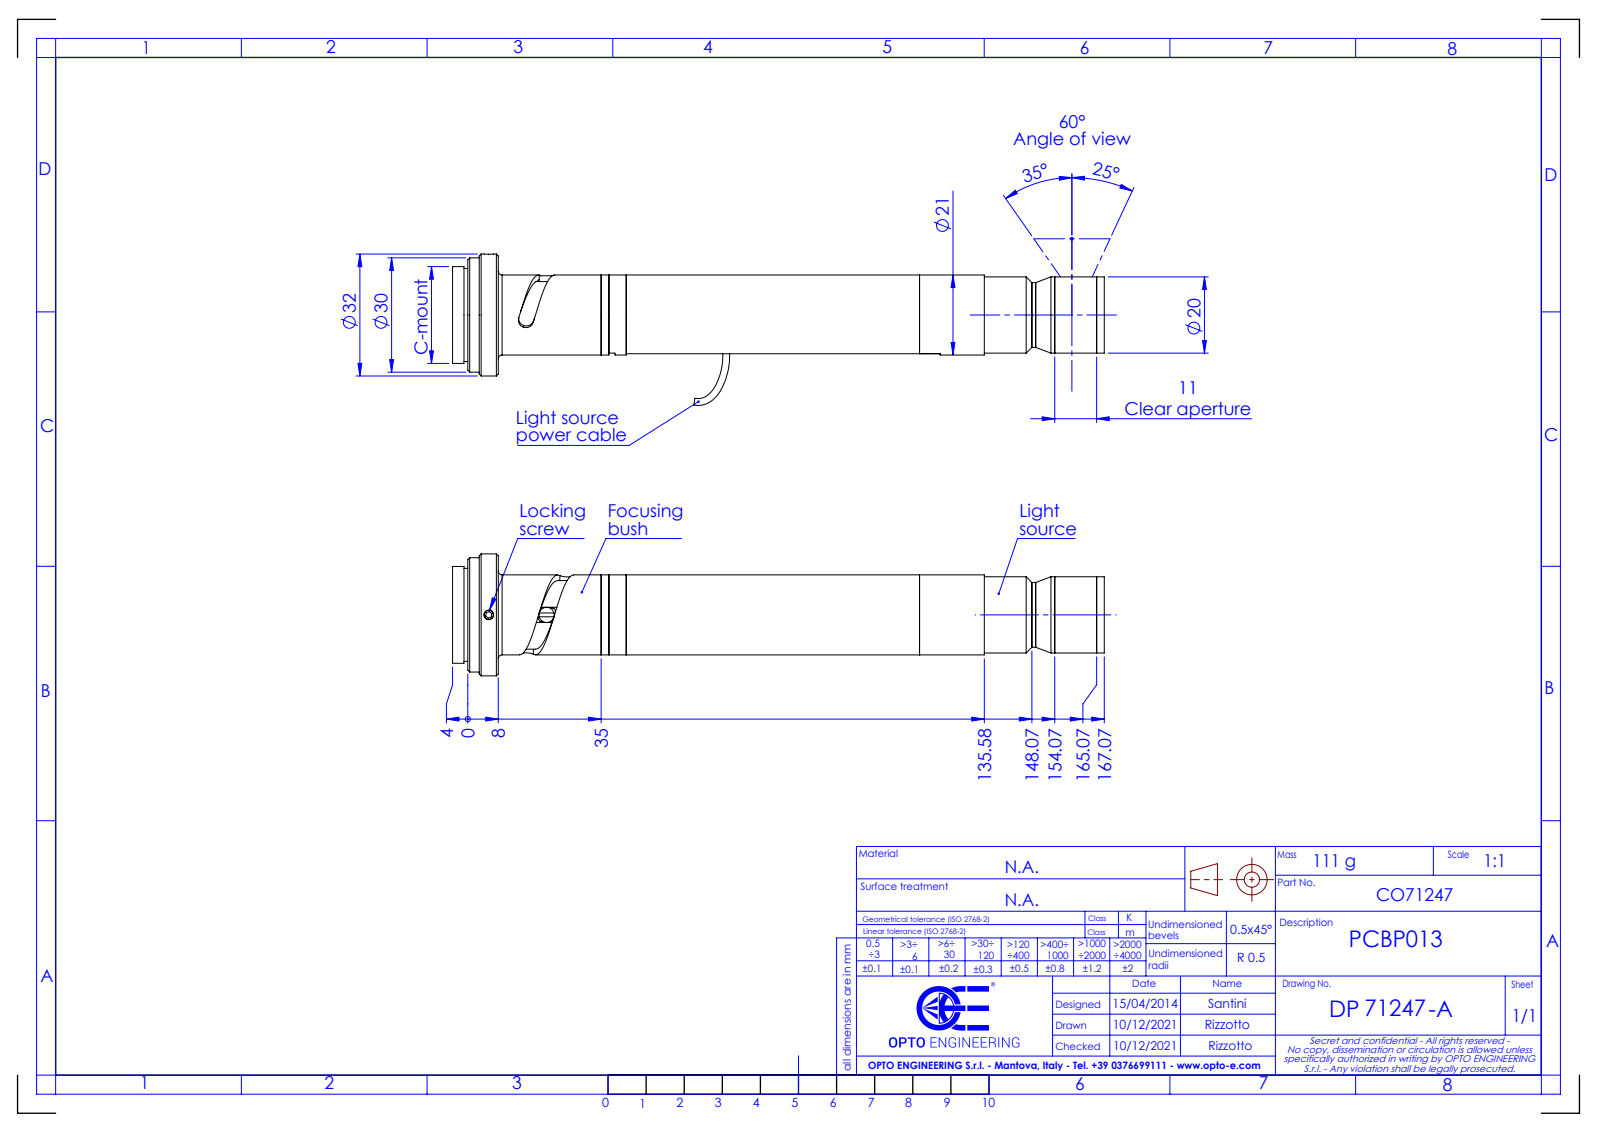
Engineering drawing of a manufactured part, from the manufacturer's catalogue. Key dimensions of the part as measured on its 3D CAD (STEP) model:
Part name (STEP PRODUCT): DP71247-A_PCBP013
STEP written by: SolidWorks 2021 (CONFIG_CONTROL_DESIGN)
Units: millimetres
Bodies: 0 solids, 117 faces (42 planar, 44 cylindrical, 31 other)
Overall size (bounding box): 171.07 × 39.73 × 32
Round holes (diameter × count): ⌀2.5 ×1
Round bosses / shafts (diameter × count): ⌀32 ×1, ⌀30 ×1, ⌀25.4 ×1, ⌀24.4 ×1, ⌀21 ×1, ⌀20 ×1, ⌀18 ×1, ⌀17 ×1
Partial cylindrical surfaces — rounded edges, fillets, slot ends (radius × count): R1 ×2
Main face-to-face distances: 115.58, 5, 110.58, 164.07, 159.07, 48.49, 34.04, 29.04, 81.54, 130.03
